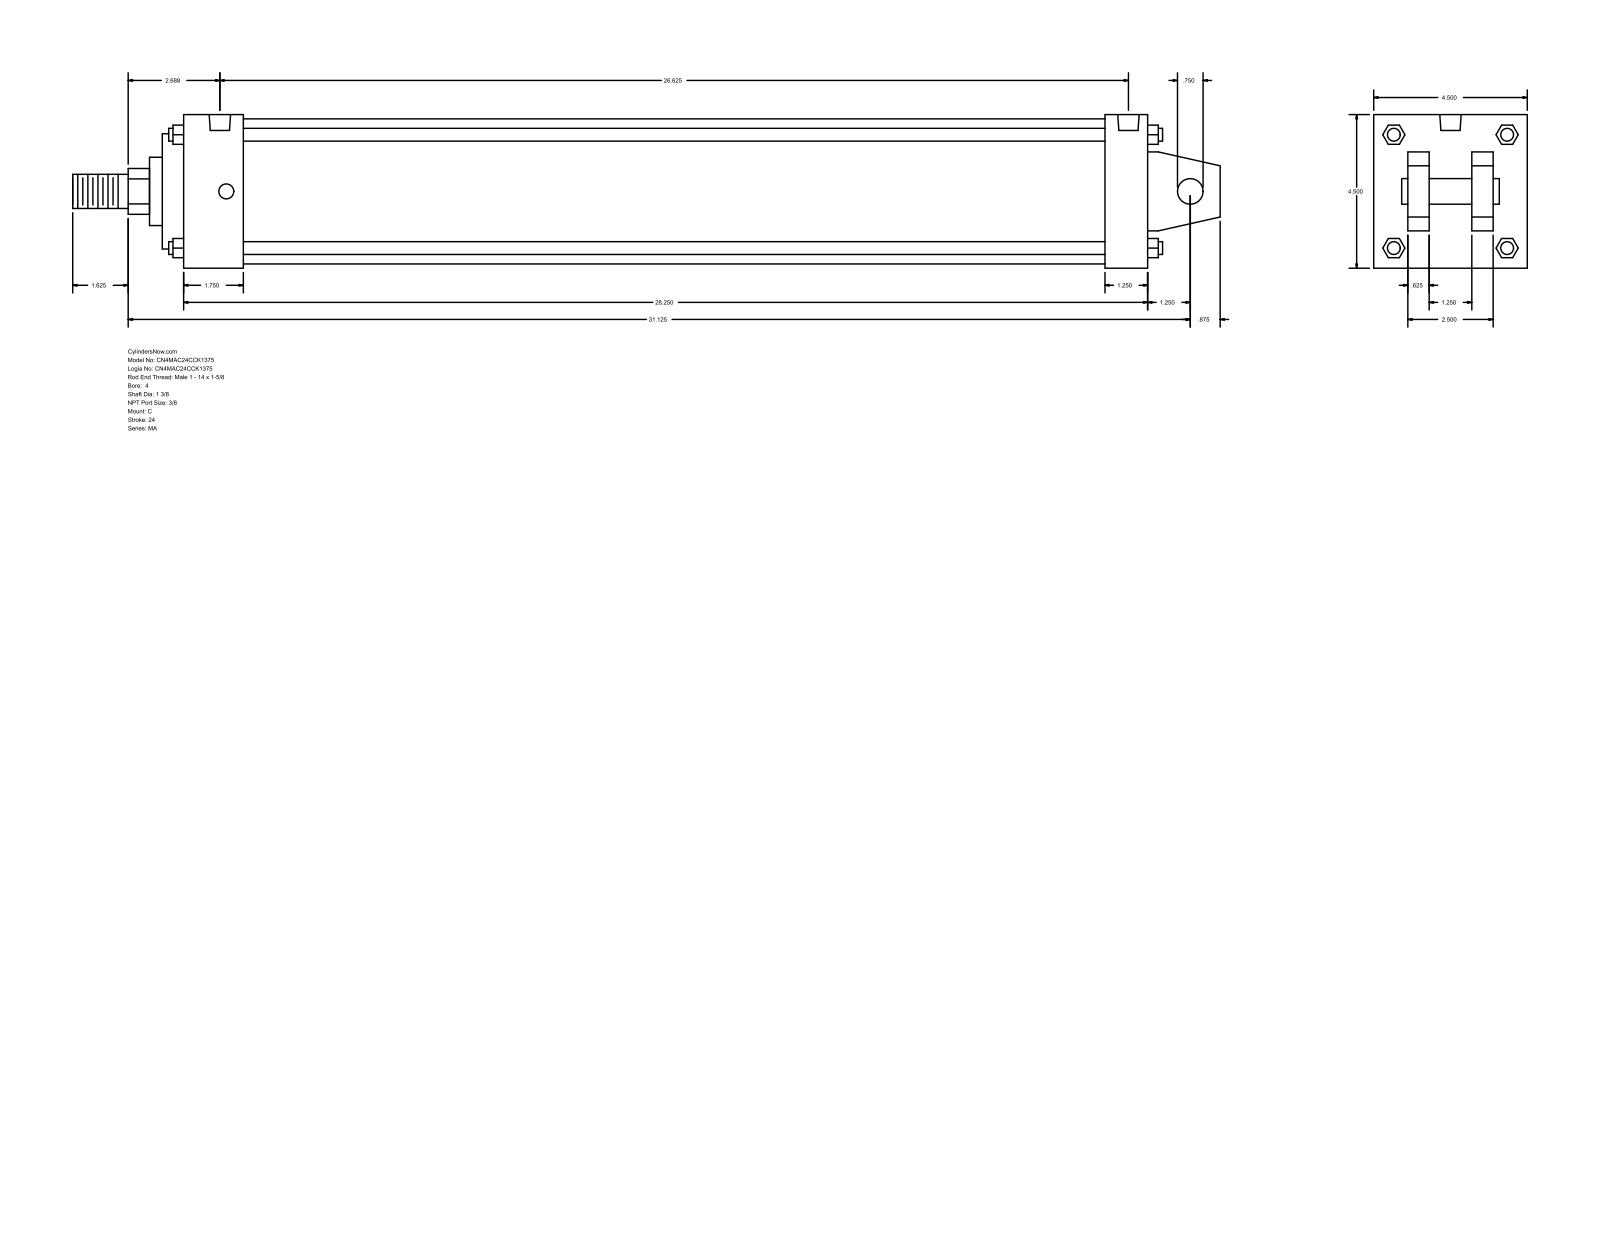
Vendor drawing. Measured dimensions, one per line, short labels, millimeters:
name: MA_C__0400_1.375
written by: GSSL Pune (CONFIG_CONTROL_DESIGN)
unit: mm
bodies: 0 solids, 141 faces (109 planar, 32 cylindrical, 0 other)
size: 854.08 × 114.3 × 114.3
holes: 4× ⌀11.11, 2× ⌀15.93
bosses: 4× ⌀9.53, 1× ⌀107.95, 1× ⌀85.72, 1× ⌀50.8, 1× ⌀34.92, 1× ⌀25.4, 1× ⌀19.05
rounds: 1× R17.06
face distances: 114.3, 15.87, 717.56, 73.03, 41.27, 25.4, 88.9, 47.63, 733.43, 701.68
hole spacings: 4.77, 666.74, 671.51, 676.28
